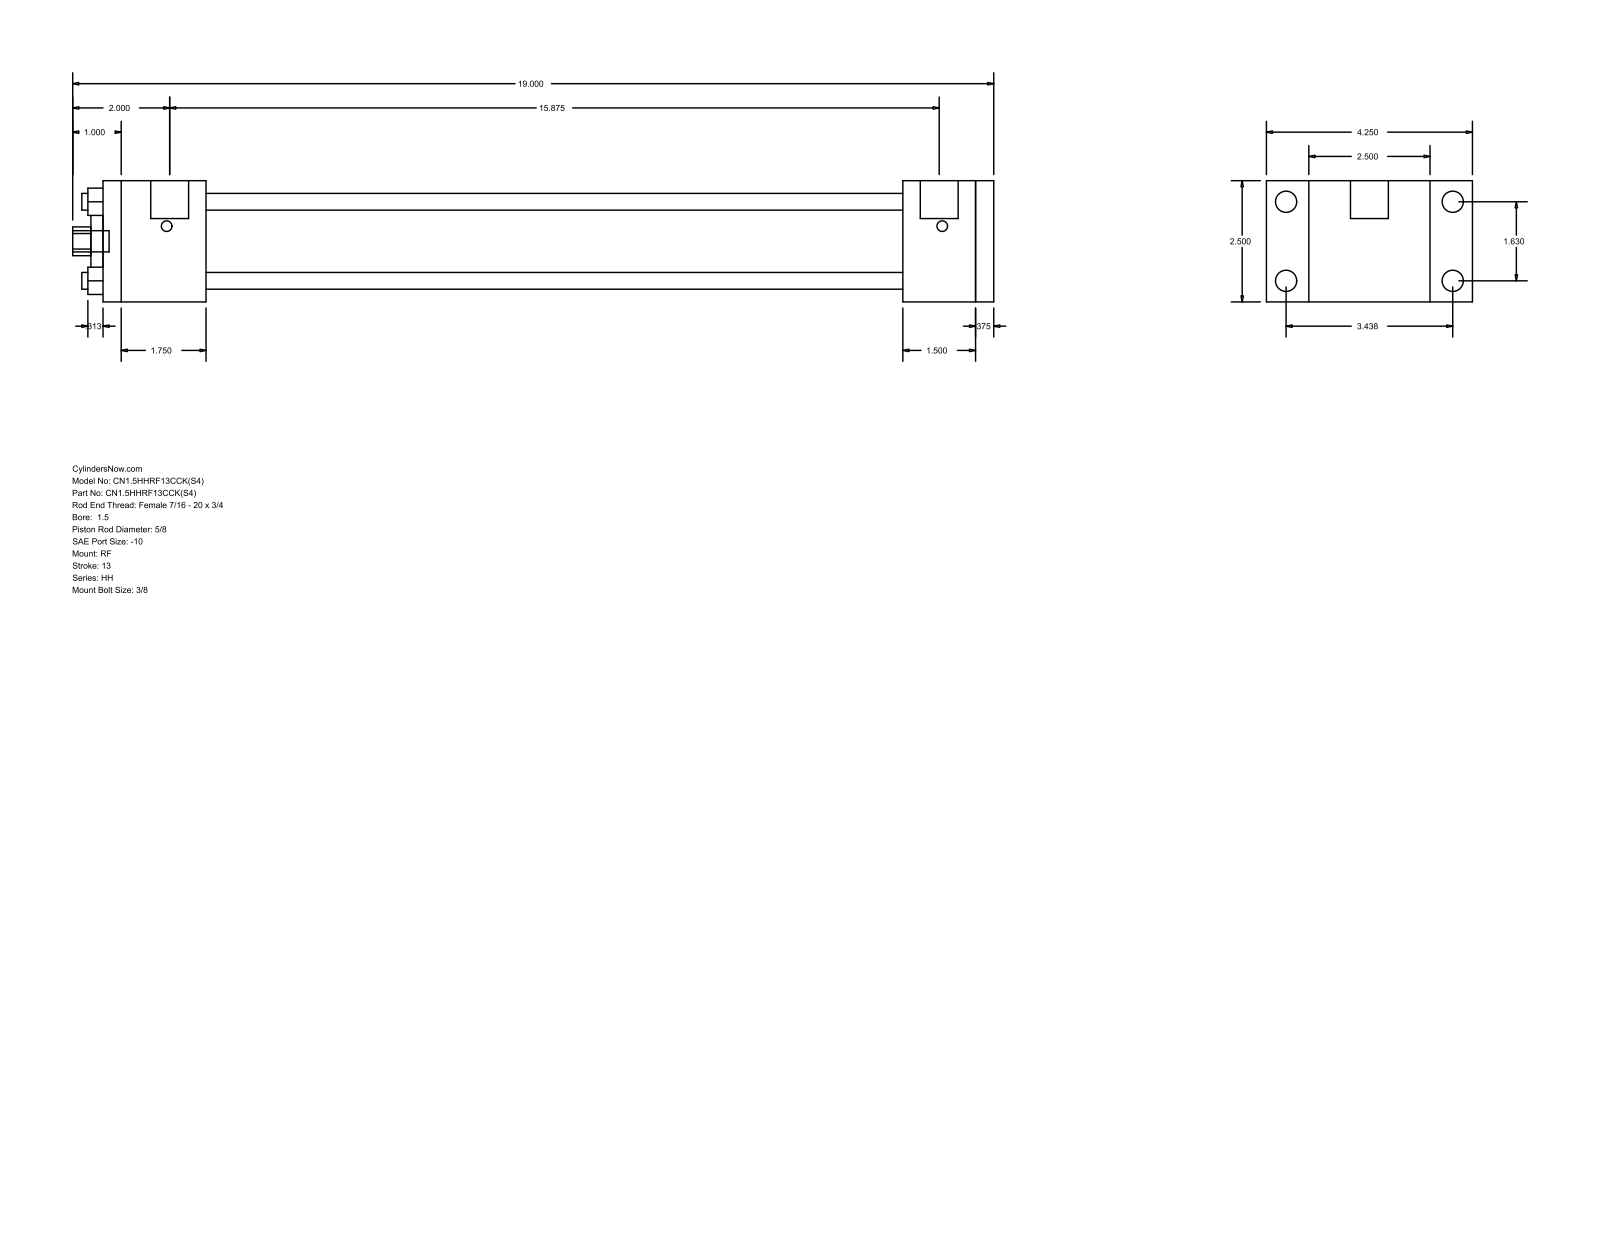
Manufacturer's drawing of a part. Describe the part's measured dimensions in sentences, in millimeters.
The part is named "HH_RF__0150_0.625". Its 3-D file was written by "GSSL Pune (CONFIG_CONTROL_DESIGN)". It is 0 solids with 92 faces: 64 planar, 28 cylindrical and 0 other. Overall it measures 482.6 by 107.95 by 63.5 millimeters. Round holes: 4 of diameter 8.76, 1 of diameter 15.88, 1 of diameter 28.57, 1 of diameter 44.45. Round bosses or shafts: 4 of diameter 11.13, 4 of diameter 5.56, 2 of diameter 19.84, 1 of diameter 11.11. Partial cylindrical surfaces (rounded edges, fillets, slot ends): 1 of radius 7.54. The main face-to-face distances are 63.5, 466.72, 9.53, 457.19, 53.97, 419.1, 365.13, 403.22, 412.75, 38.09. The hole center spacings are 29.27, 41.4, 58.55.
